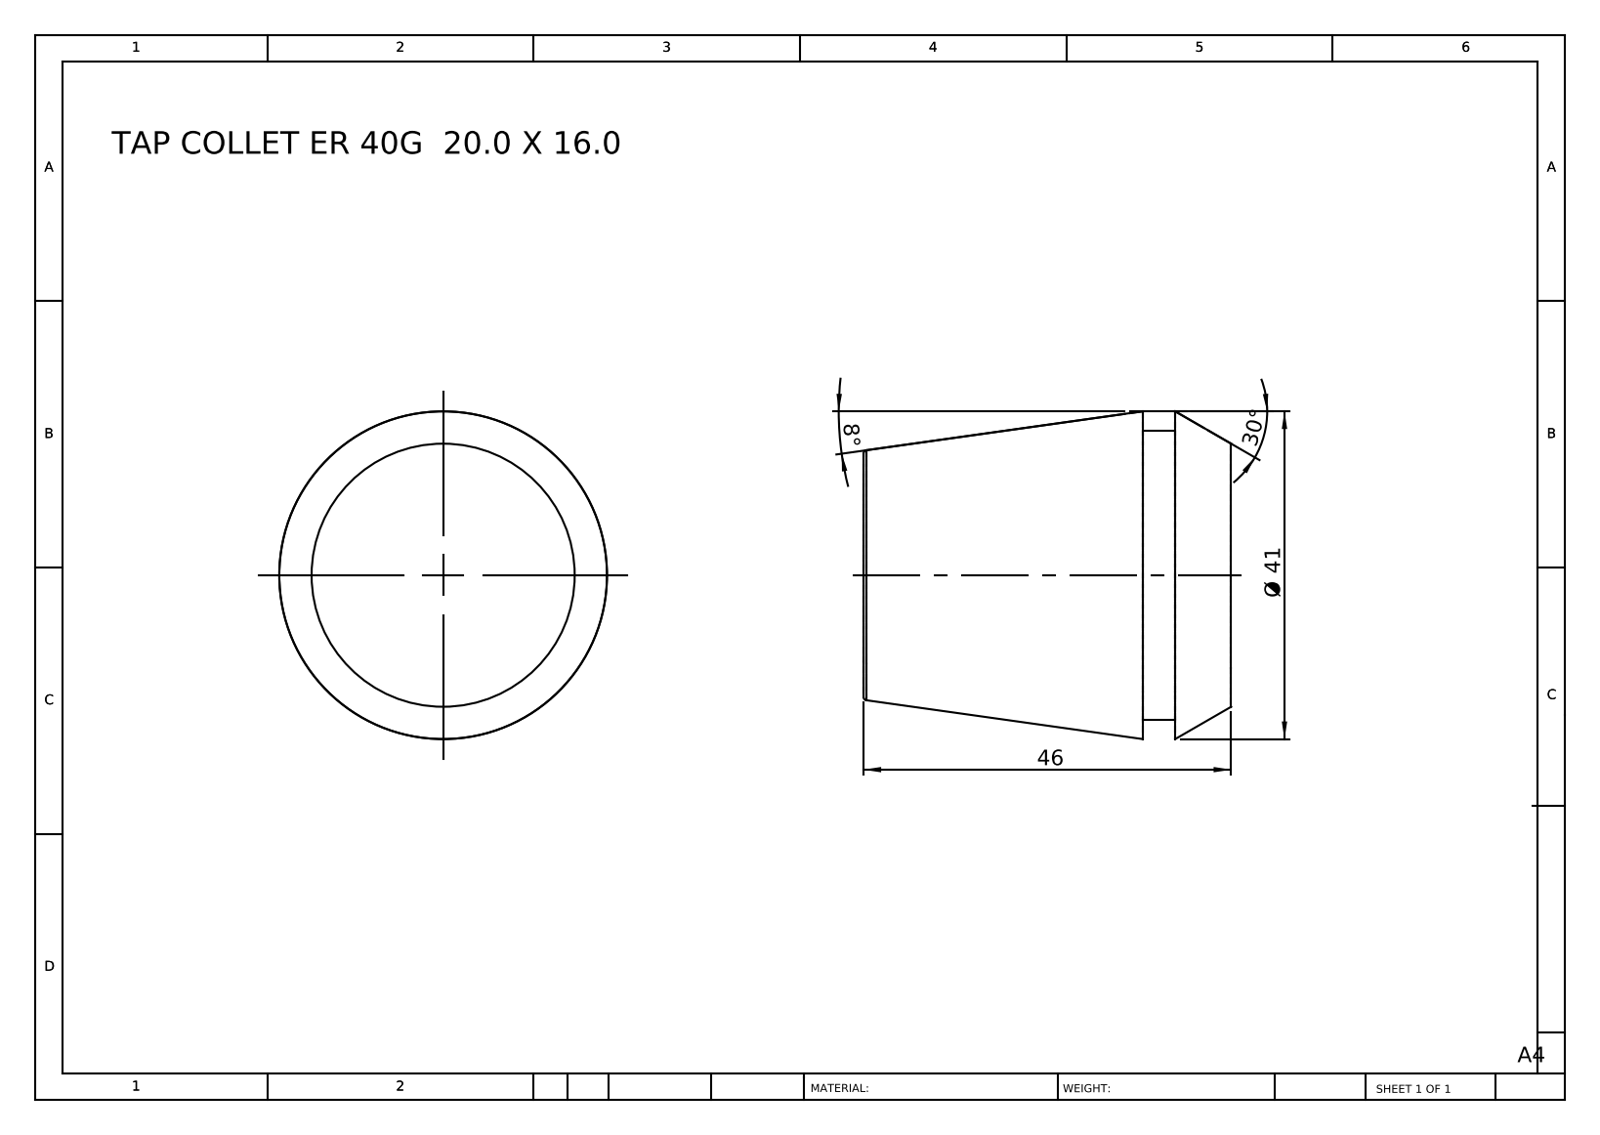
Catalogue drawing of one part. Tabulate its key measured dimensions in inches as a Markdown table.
| quantity | value |
| --- | --- |
| part name | TAP COLLET ER 40G 20.0 X 16.0 |
| STEP written by | SolidWorks 2014 (CONFIG_CONTROL_DESIGN) |
| units | inches |
| bodies | 1 solid, 12 faces (4 planar, 2 cylindrical, 6 other) |
| overall size | 1.811 × 1.614 × 1.614 |
| volume | 2.91 in³ |
| surface area | 11.76 in² |
| round bosses / shafts (diameter × count) | 1.425 × 1 |
| main face-to-face distances | 1.811, 0.437, 1.374, 0.276, 0.161, 1.535 |
